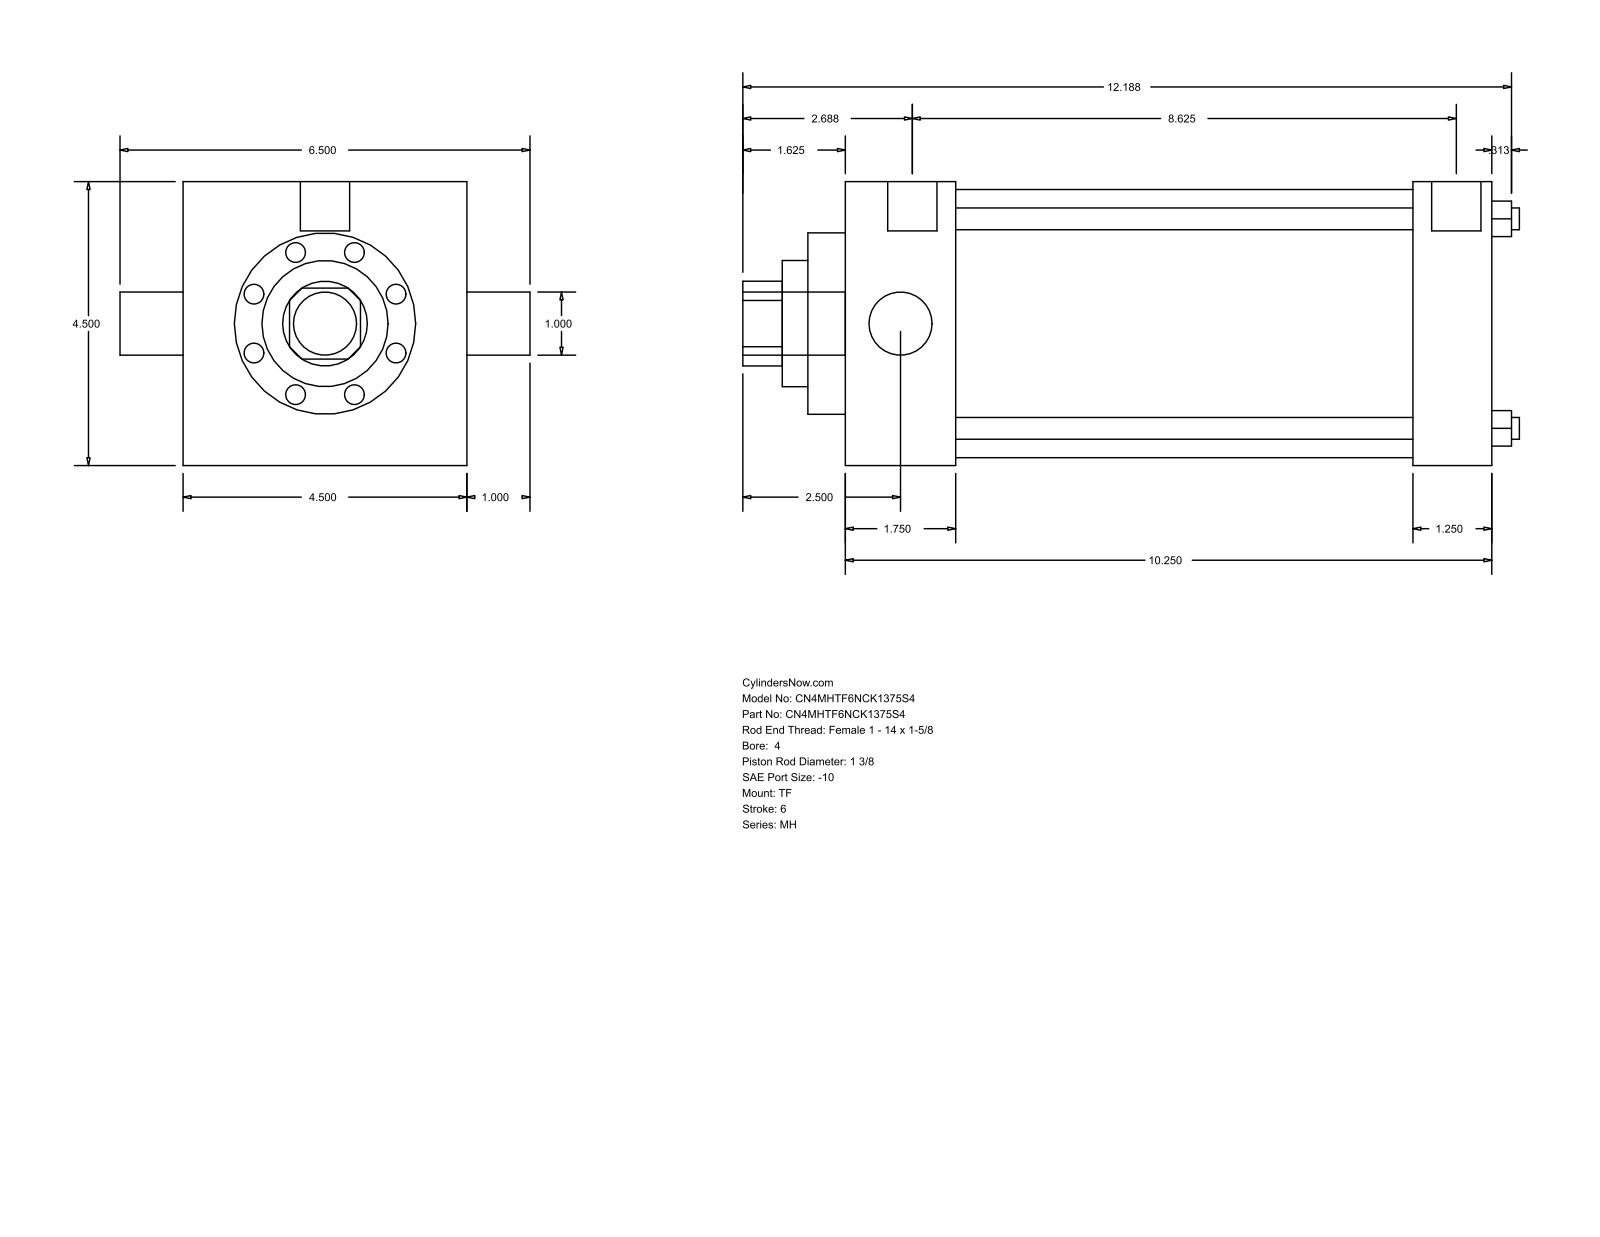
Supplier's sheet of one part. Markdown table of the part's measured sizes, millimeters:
| quantity | value |
| --- | --- |
| part name | MH_TF__0400_1.375 |
| STEP written by | GSSL Pune (CONFIG_CONTROL_DESIGN) |
| units | millimeters |
| bodies | 0 solids, 86 faces (61 planar, 25 cylindrical, 0 other) |
| overall size | 312.74 × 165.1 × 114.3 |
| round holes (diameter × count) | 8.76 × 4, 25.4 × 1, 34.92 × 1, 50.8 × 1, 73.03 × 1, 107.95 × 1 |
| round bosses / shafts (diameter × count) | 8.73 × 3, 19.84 × 2, 25.4 × 1 |
| partial cylindrical surfaces (radius × count) | 17.06 × 1 |
| main face-to-face distances | 114.3, 260.35, 44.45, 215.9, 228.61, 184.16, 31.74, 15.08, 59.53, 243.69 |
| hole center spacings | 59.62, 84.32, 119.25 |
